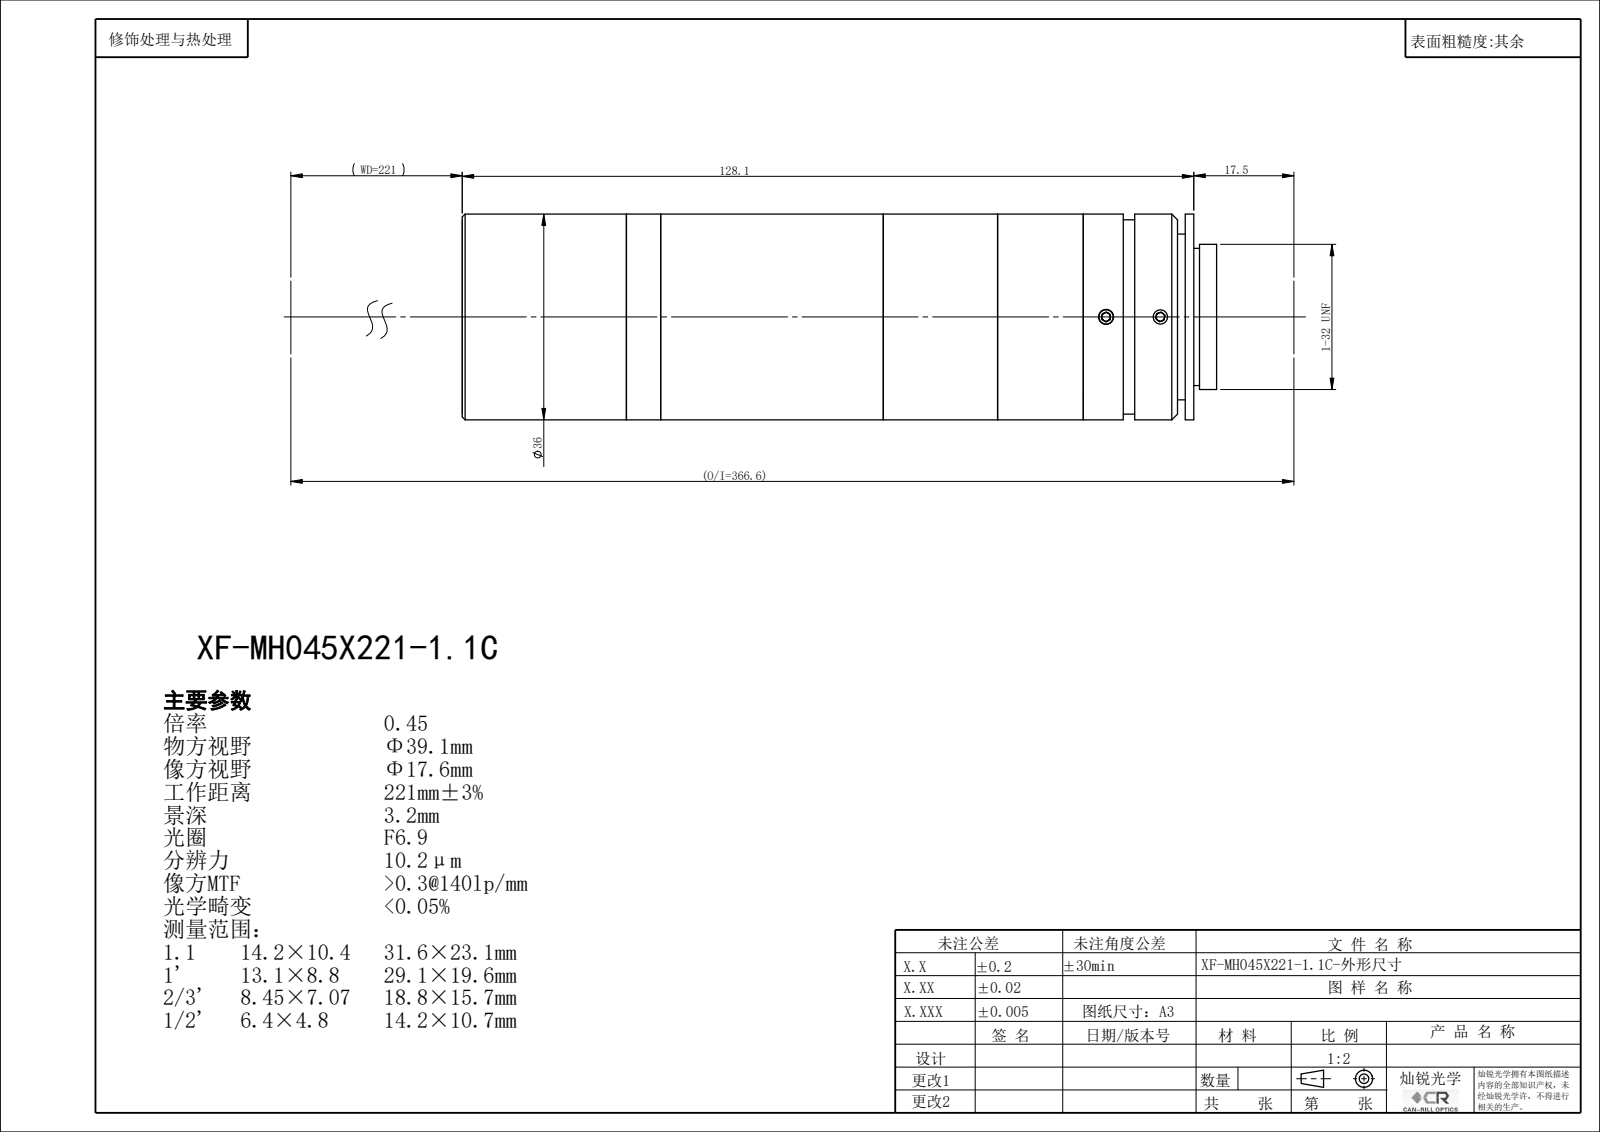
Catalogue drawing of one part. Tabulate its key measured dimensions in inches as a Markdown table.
| quantity | value |
| --- | --- |
| part name | XF-MH045X221-1.1C |
| STEP written by | SolidWorks 2022 (CONFIG_CONTROL_DESIGN) |
| units | inches |
| bodies | 0 solids, 136 faces (72 planar, 42 cylindrical, 22 other) |
| overall size | 5.2 × 1.417 × 1.417 |
| round holes (diameter × count) | 0.098 × 3, 0.882 × 1, 0.945 × 1, 1.024 × 1, 1.039 × 1, 1.157 × 1, 1.315 × 1, 1.358 × 1 |
| round bosses / shafts (diameter × count) | 1.417 × 1, 1.339 × 1, 1 × 1 |
| main face-to-face distances | 0.762, 0.059, 0.703, 0.591, 1.293, 1.352, 0.787, 1.378, 2.081, 2.14 |
